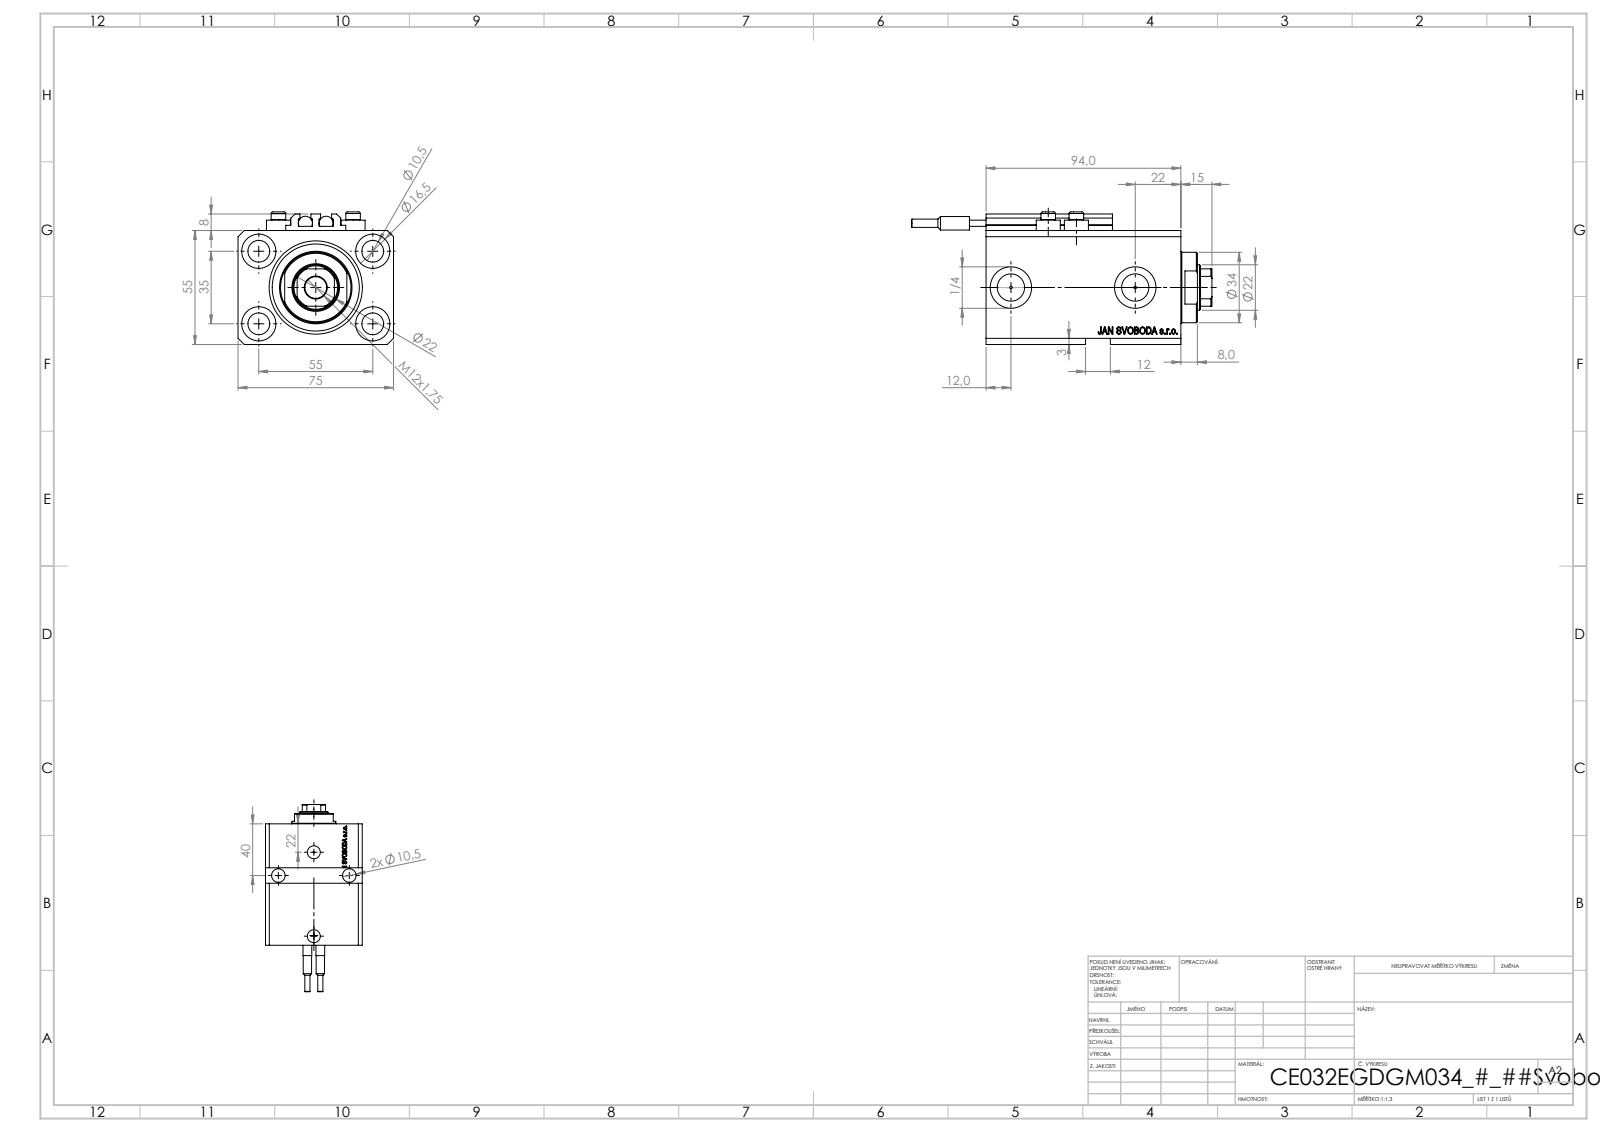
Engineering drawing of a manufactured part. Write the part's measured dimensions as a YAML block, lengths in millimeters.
part_name: "V250CE_VC_E; ALLEN BOLT V250CE; V250CE_E_Body; SWITCH_V250CE (+1 more)"
step_written_by: "SolidWorks 2019 (CONFIG_CONTROL_DESIGN)"
units: millimeters
bodies: {solids: 10, faces: 1132, planar: 550, cylindrical: 150, other: 432}
overall_size: [145, 75, 64]
volume: 332325
surface_area: 87537
round_holes:
  - {diameter: 10.5, count: 7}
  - {diameter: 1.25, count: 4}
  - {diameter: 4, count: 4}
  - {diameter: 16.5, count: 4}
  - {diameter: 10, count: 2}
  - {diameter: 13.16, count: 2}
  - {diameter: 20, count: 2}
  - {diameter: 22, count: 1}
  - {diameter: 32, count: 1}
  - {diameter: 45, count: 1}
round_bosses_or_shafts:
  - {diameter: 11.6, count: 4}
  - {diameter: 7, count: 4}
  - {diameter: 6.8, count: 2}
  - {diameter: 6.5, count: 2}
  - {diameter: 4, count: 2}
  - {diameter: 34, count: 1}
partial_cylinders:
  - {radius: 0.2, count: 10}
  - {radius: 10.5, count: 1}
face_to_face_distances: [55, 75, 3, 15, 57, 94, 79, 9.9, 69.1, 84.1]
hole_center_spacings: [32.6, 55, 13.6, 14.09, 25.81, 28.79, 29.21, 32.87]
